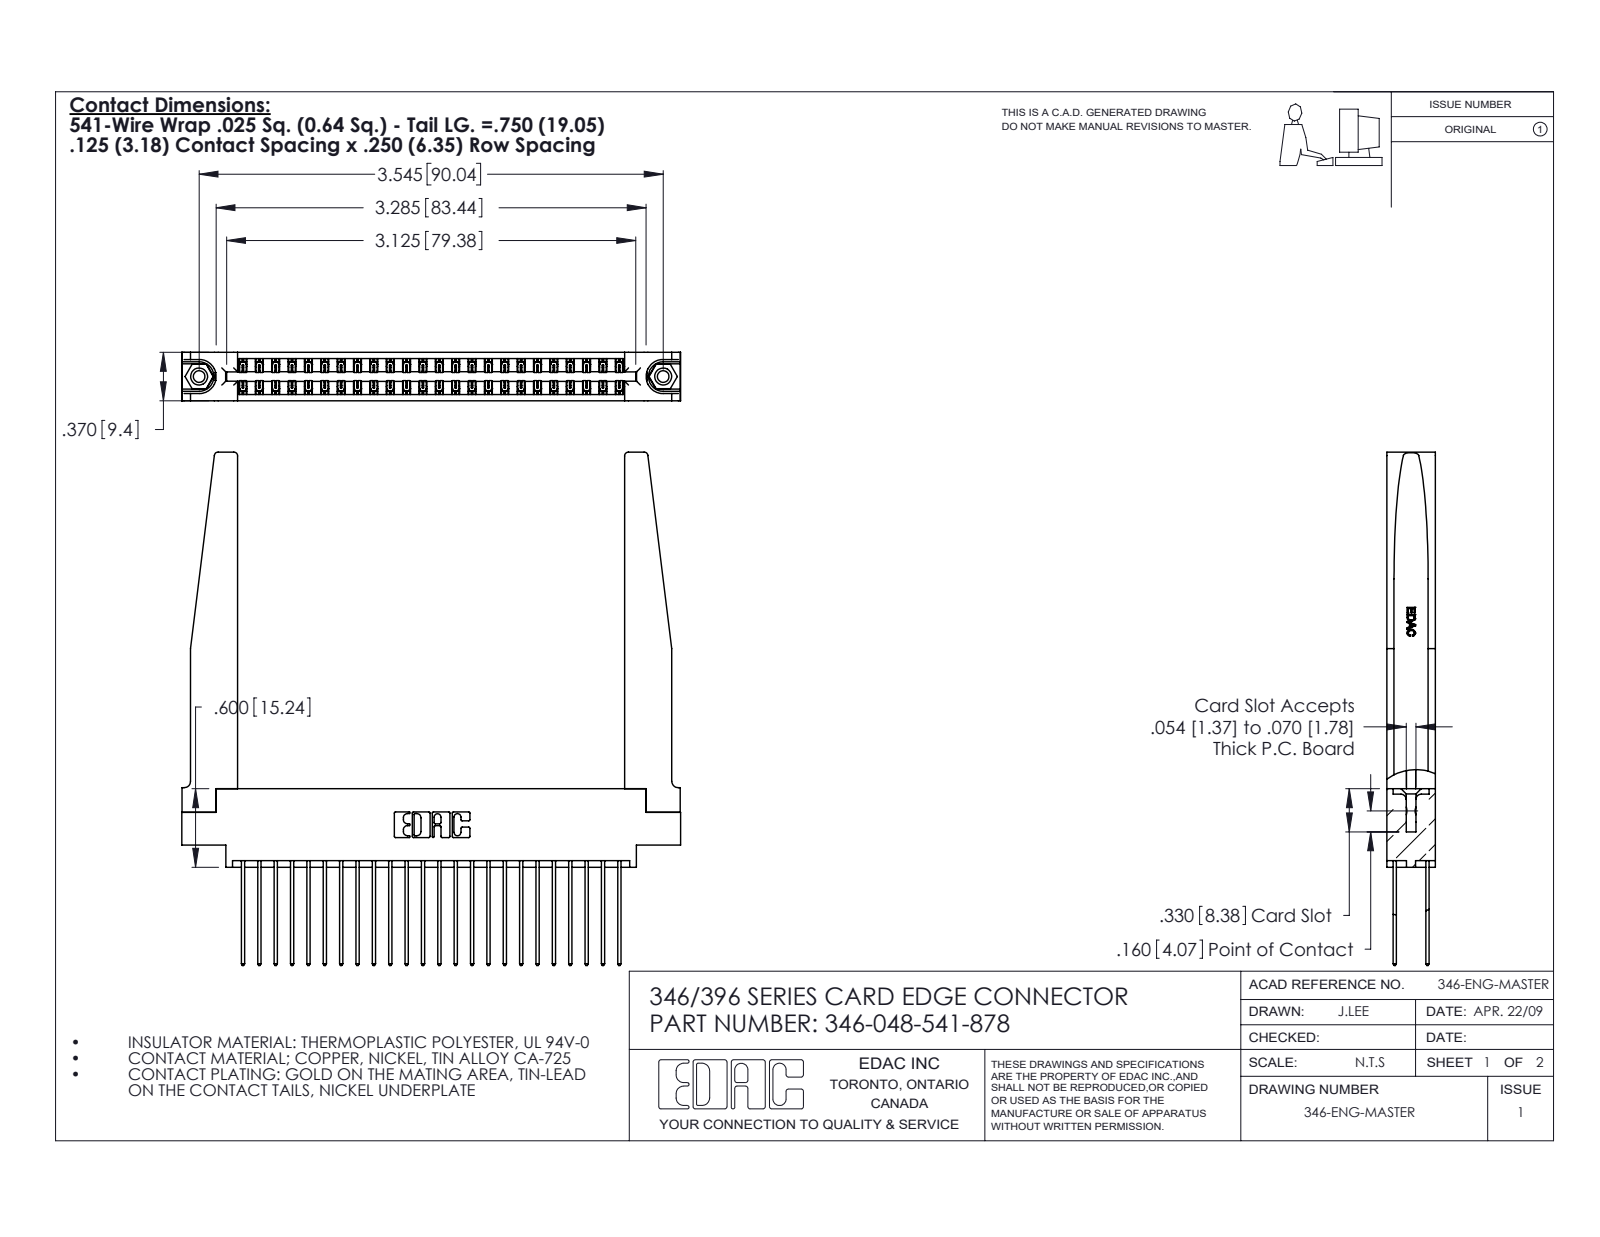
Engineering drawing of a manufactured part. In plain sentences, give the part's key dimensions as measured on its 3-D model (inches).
The part is named "345-292-001_345-293-141; 345-250-001_345-250-001-102; 346 Part_0.170 Offset - 0.156 Dia-TH; 346-220-078_345-220-078 (+1 more)". Its 3-D file was written by "SolidWorks 2020 (CONFIG_CONTROL_DESIGN)". It is 53 solids with 2870 faces: 1916 planar, 902 cylindrical and 52 other. Overall it measures 3.92 by 3.81 by 0.37 inches. Its volume is 0.995 cubic inches and its surface area 32.1 square inches. Round holes: 2 of diameter 0.089, 2 of diameter 0.125, 2 of diameter 0.156, 1 of diameter 0.064. Round bosses or shafts: 2 of diameter 0.155. Partial cylindrical surfaces (rounded edges, fillets, slot ends): 72 of radius 0.006, 48 of radius 0.01, 22 of radius 0.01, 8 of radius 0.03, 6 of radius 0.007, 6 of radius 0.031, 3 of radius 0.026, 2 of radius 0.014. The main face-to-face distances are 0.37, 0.048, 0.322, 0.072, 0.25, 0.298, 0.025, 0.148, 0.15, 0.275. The hole center spacings are 0.246, 3.337, 3.545.
